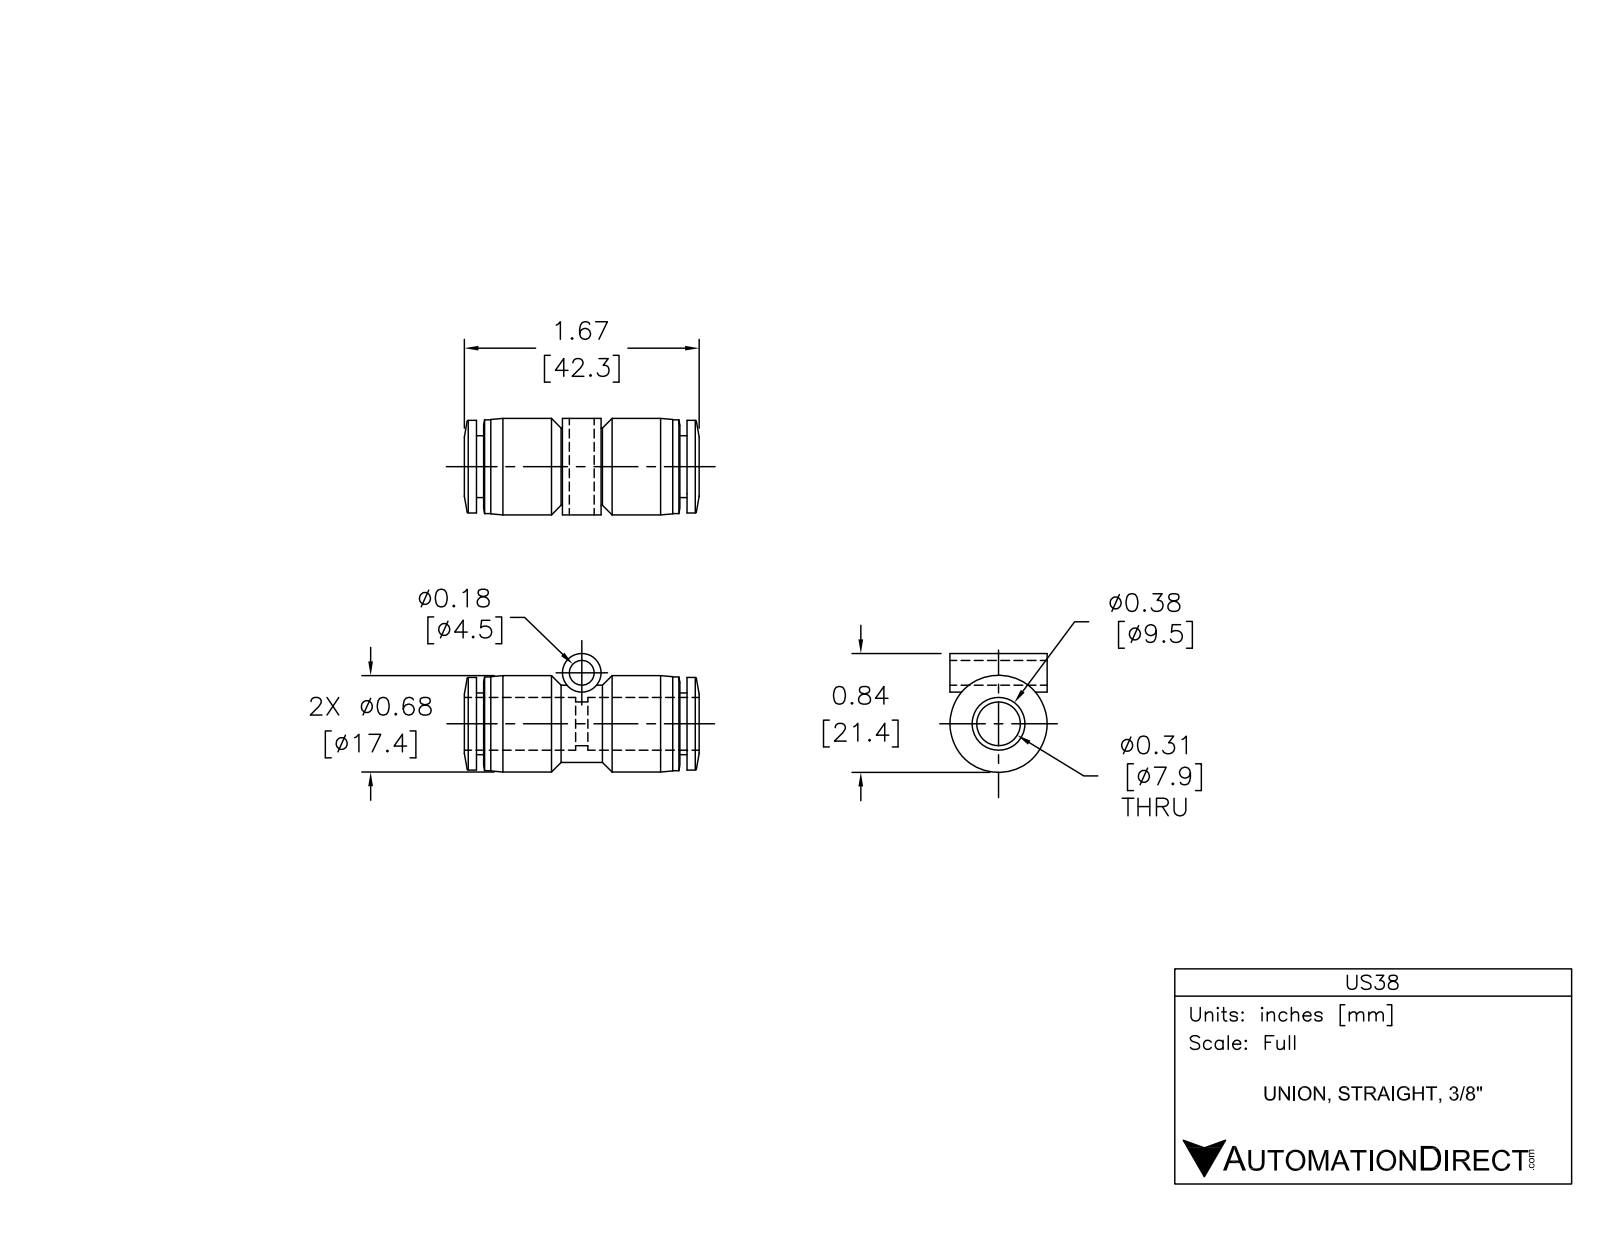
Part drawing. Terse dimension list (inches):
name: US38
written by: SolidWorks 2015 (AUTOMOTIVE_DESIGN)
unit: in
bodies: 1 solid, 66 faces (10 planar, 28 cylindrical, 28 other)
size: 1.677 × 0.846 × 0.689
volume: 0.37 in³; area: 7.605 in²
holes: 1× ⌀0.177, 1× ⌀0.315, 1× ⌀0.386
bosses: 1× ⌀0.689, 1× ⌀0.669, 1× ⌀0.661, 1× ⌀0.551, 1× ⌀0.441, 1× ⌀0.276
face distances: 0.051, 1.453, 1.504, 1.402, 0.705, 0.799, 0.654, 0.748, 0.094, 0.689
